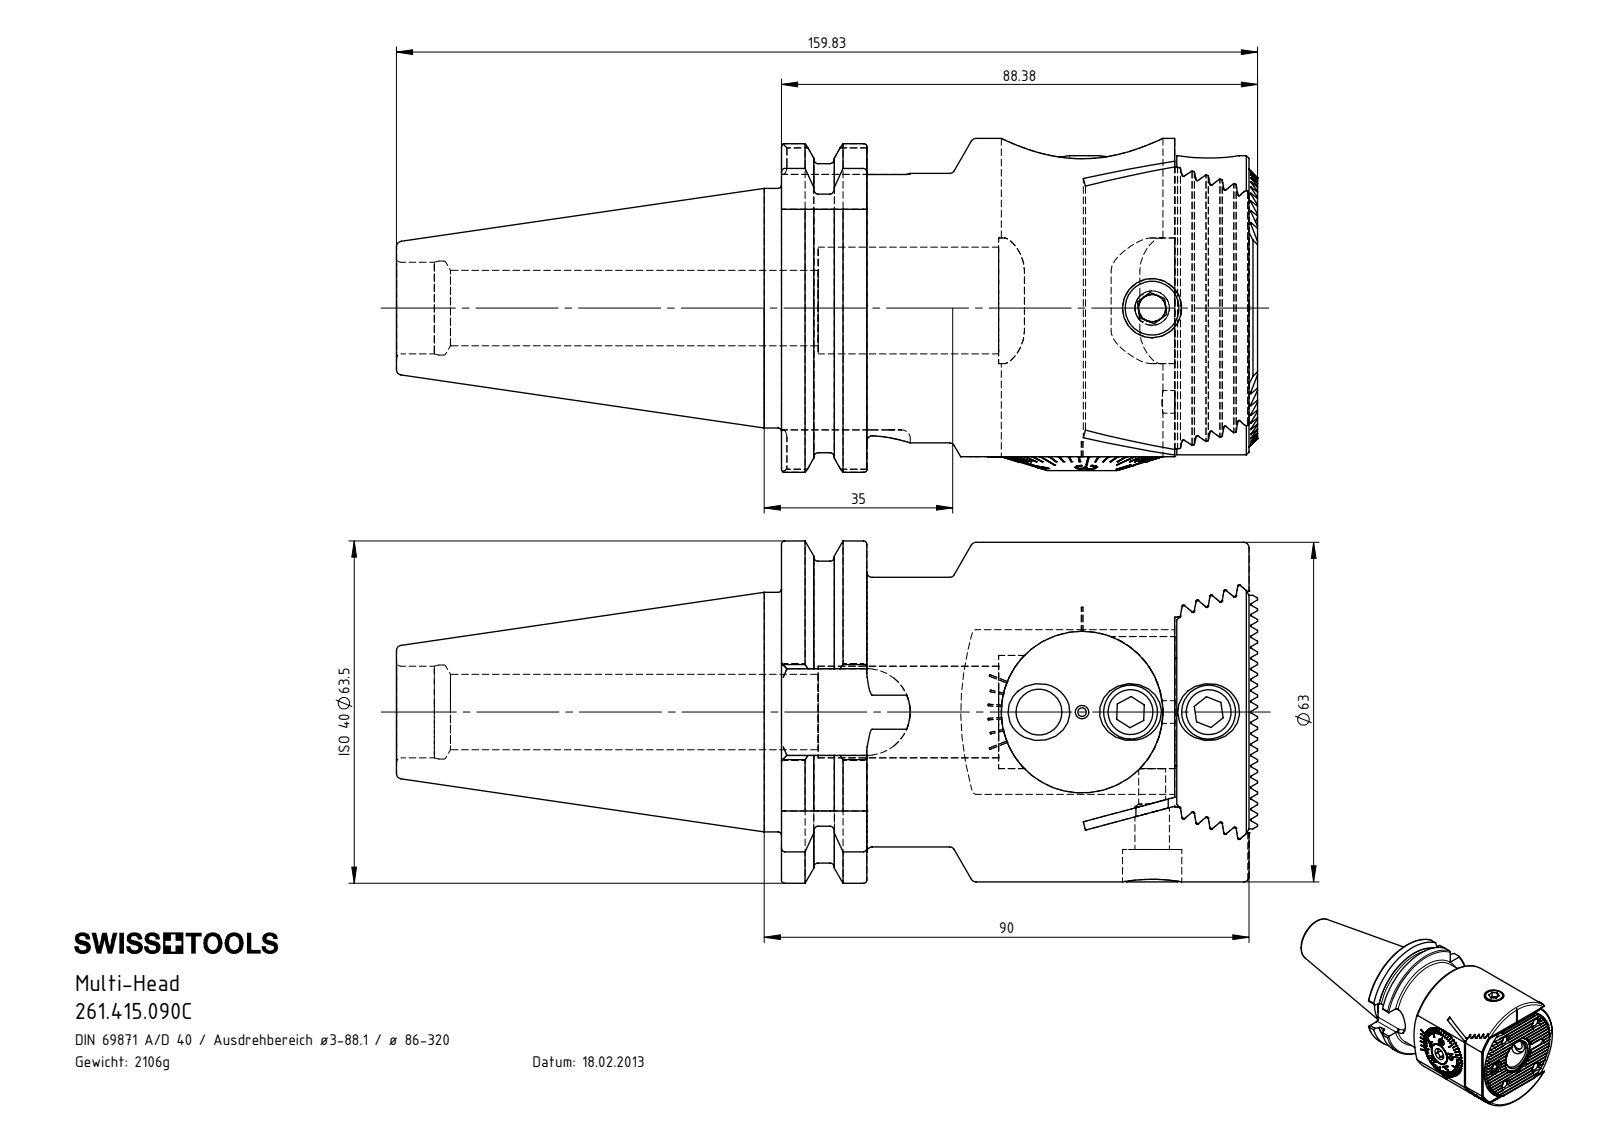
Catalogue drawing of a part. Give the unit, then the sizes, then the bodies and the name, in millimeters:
Units: millimetres
Overall size (bounding box): 159.83 × 63.5 × 61.95
Round holes (diameter × count): ⌀4.2 ×5, ⌀8.5 ×4, ⌀6.8 ×3, ⌀11 ×3, ⌀14 ×2, ⌀20 ×2, ⌀1 ×1, ⌀1.6 ×1, ⌀3.3 ×1, ⌀5 ×1, ⌀6.4 ×1, ⌀8 ×1
Round bosses / shafts (diameter × count): ⌀10 ×3, ⌀63 ×1, ⌀50 ×1, ⌀44.45 ×1, ⌀30 ×1, ⌀29.98 ×1, ⌀29.9 ×1, ⌀25 ×1
Partial cylindrical surfaces — rounded edges, fillets, slot ends (radius × count): R0.14 ×21, R0.2 ×20, R1.6 ×8, R6 ×6, R4 ×2, R31 ×2, R2 ×1, R7 ×1
Main face-to-face distances: 2.38, 0.4, 1.73, 73, 73.4, 7.15, 4.77, 4.76, 8.66, 5.2
Hole centre spacings: 16.73, 18.03, 20.52, 24, 30, 34.8, 38.42, 7.28
Volume: 268 319 mm³ · Surface area: 74 290 mm²
Bodies: 14 solids, 1118 faces (556 planar, 253 cylindrical, 309 other)
Part name (STEP PRODUCT): MH1-BG1.001.049; A55-BG1.012.007_B; MH1-BG1.001.049_B; A55-BG2.015.007_A (+8 more)
STEP written by: SolidWorks 2017 (CONFIG_CONTROL_DESIGN)
